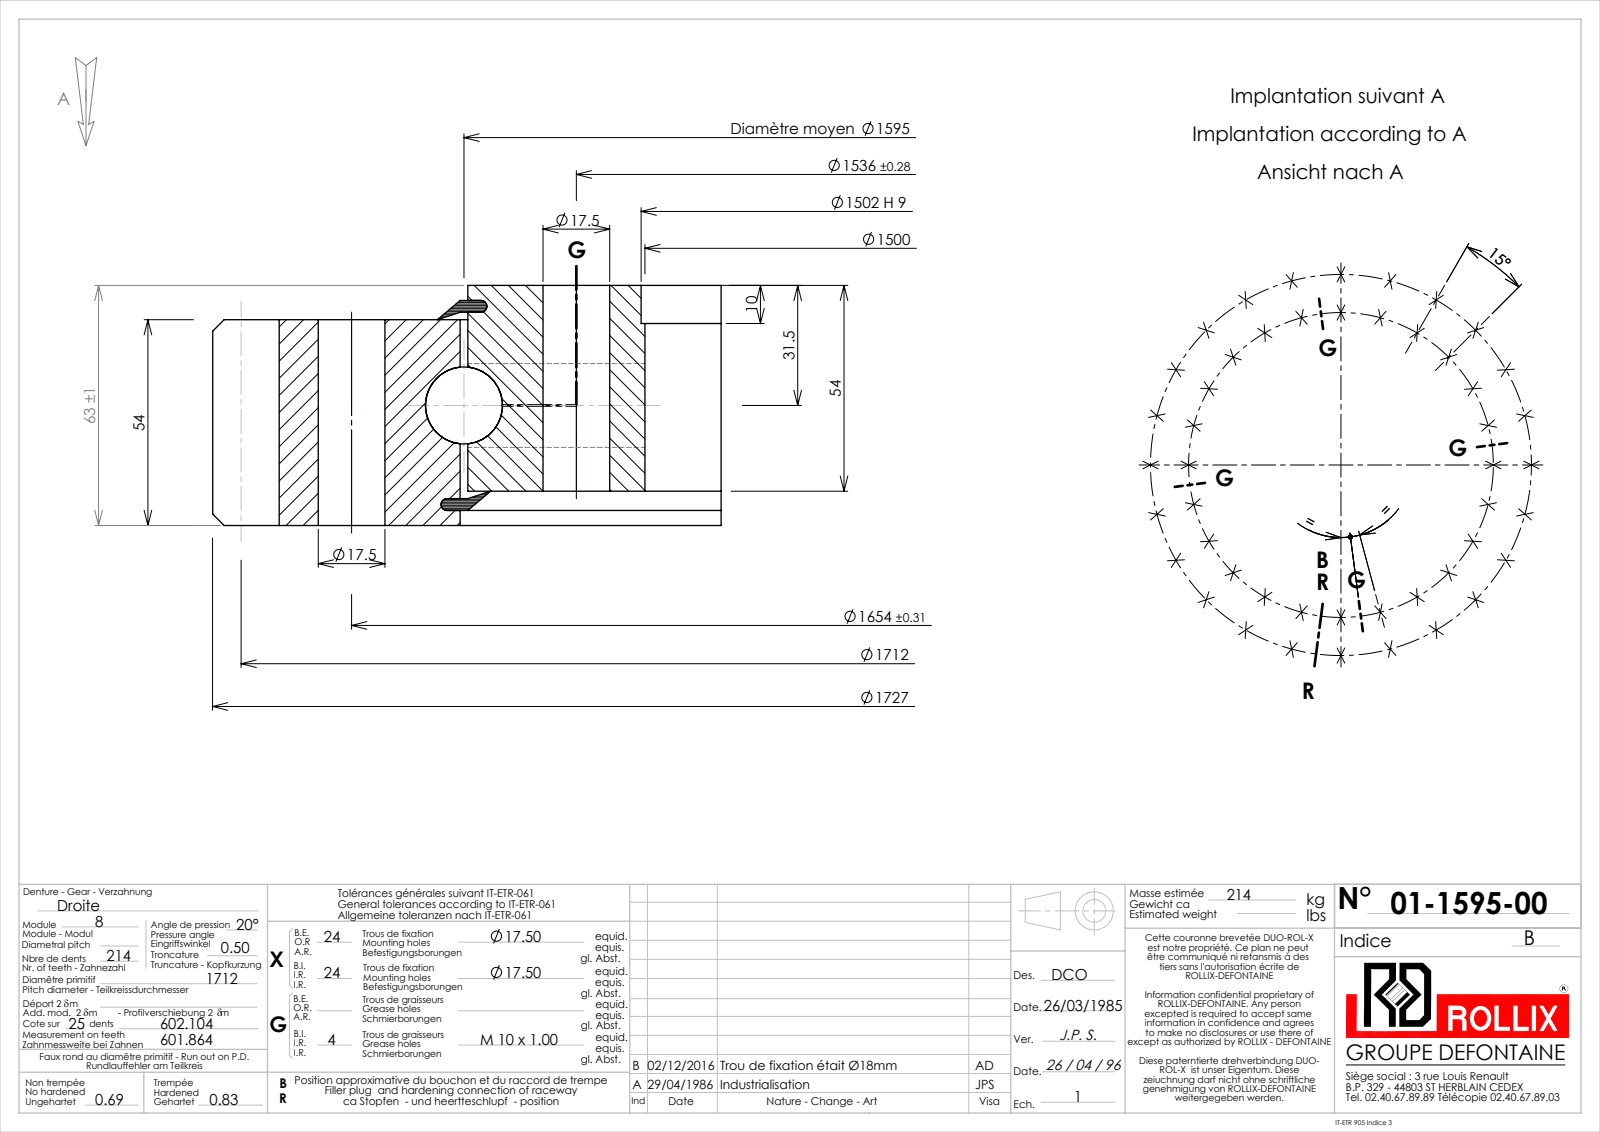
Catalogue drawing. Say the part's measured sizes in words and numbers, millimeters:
The part is named "01-1595-00". Its 3-D file was written by "SolidWorks 2016 (CONFIG_CONTROL_DESIGN)". It is 5 solids with 1454 faces: 441 planar, 549 cylindrical and 464 other. Overall it measures 1727 by 1726.91 by 63 millimeters. Its volume is 26 220 000 cubic millimeters and its surface area 3 011 000 square millimeters. Round holes: 48 of diameter 17.5, 4 of diameter 9, 1 of diameter 1500, 1 of diameter 1502, 1 of diameter 1597.02. Round bosses or shafts: 1 of diameter 1592.98. Partial cylindrical surfaces (rounded edges, fillets, slot ends): 1 of radius 846, 1 of radius 863.5. The main face-to-face distances are 54, 9, 45, 63, 7.05, 55.95, 1.95, 46.95, 3.95, 59.05. The hole center spacings are 827, 215.89, 632.96, 1006.89, 1597.64, 1639.85, 1169.55, 428.09.
